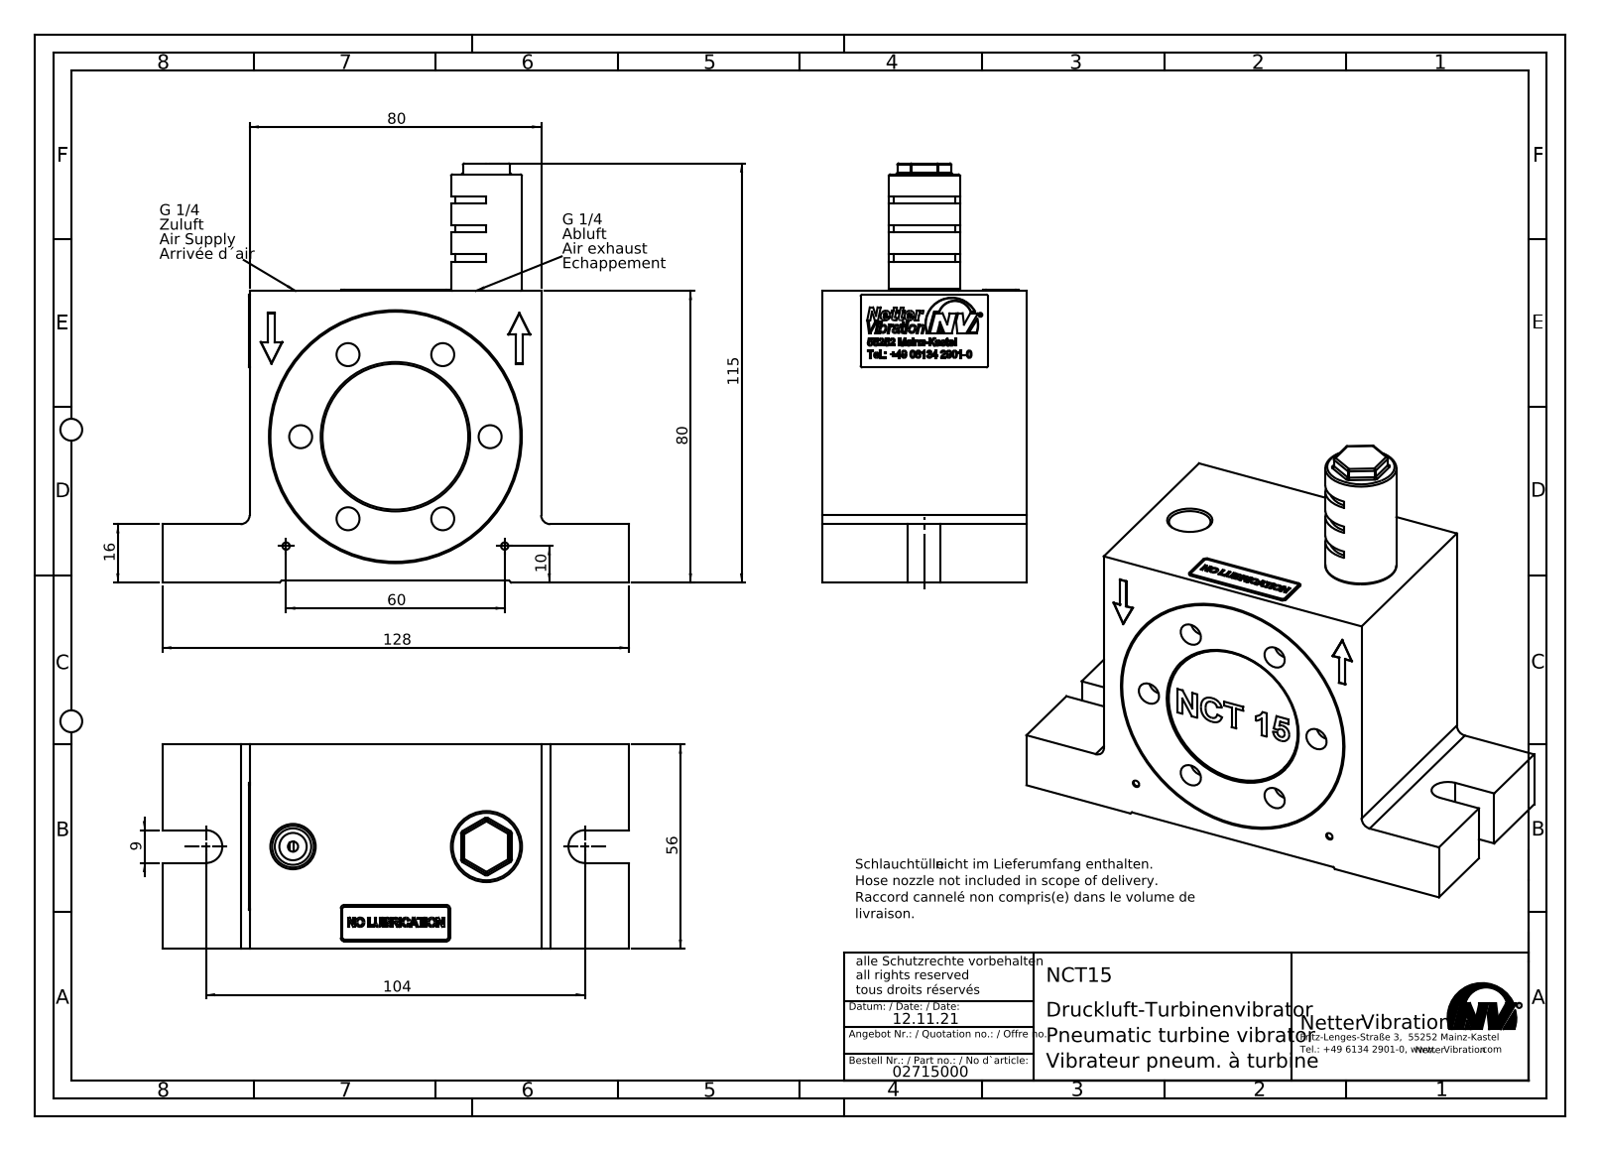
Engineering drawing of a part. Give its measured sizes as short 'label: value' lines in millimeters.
name: NCT 15 Turbinenvibrator #02715000
written by: SolidWorks 2015 (AUTOMOTIVE_DESIGN)
unit: mm
bodies: 2 solids, 307 faces (195 planar, 65 cylindrical, 47 other)
size: 128 × 115 × 56.25
volume: 403 148 mm³; area: 42 769 mm²
holes: 6× ⌀6.3, 2× ⌀2, 2× ⌀11.45, 1× ⌀41
bosses: 1× ⌀40, 1× ⌀19.5, 1× ⌀13.16
rounds: 22× R0.5, 4× R1, 2× R2.5, 2× R4.5, 1× R8.5
face distances: 80, 0.5, 56, 79.5, 16, 15.5, 64, 56.25, 24, 104
hole spacings: 26, 45.03, 18.57, 30.27, 42.43, 43.65, 45.04, 52.01
